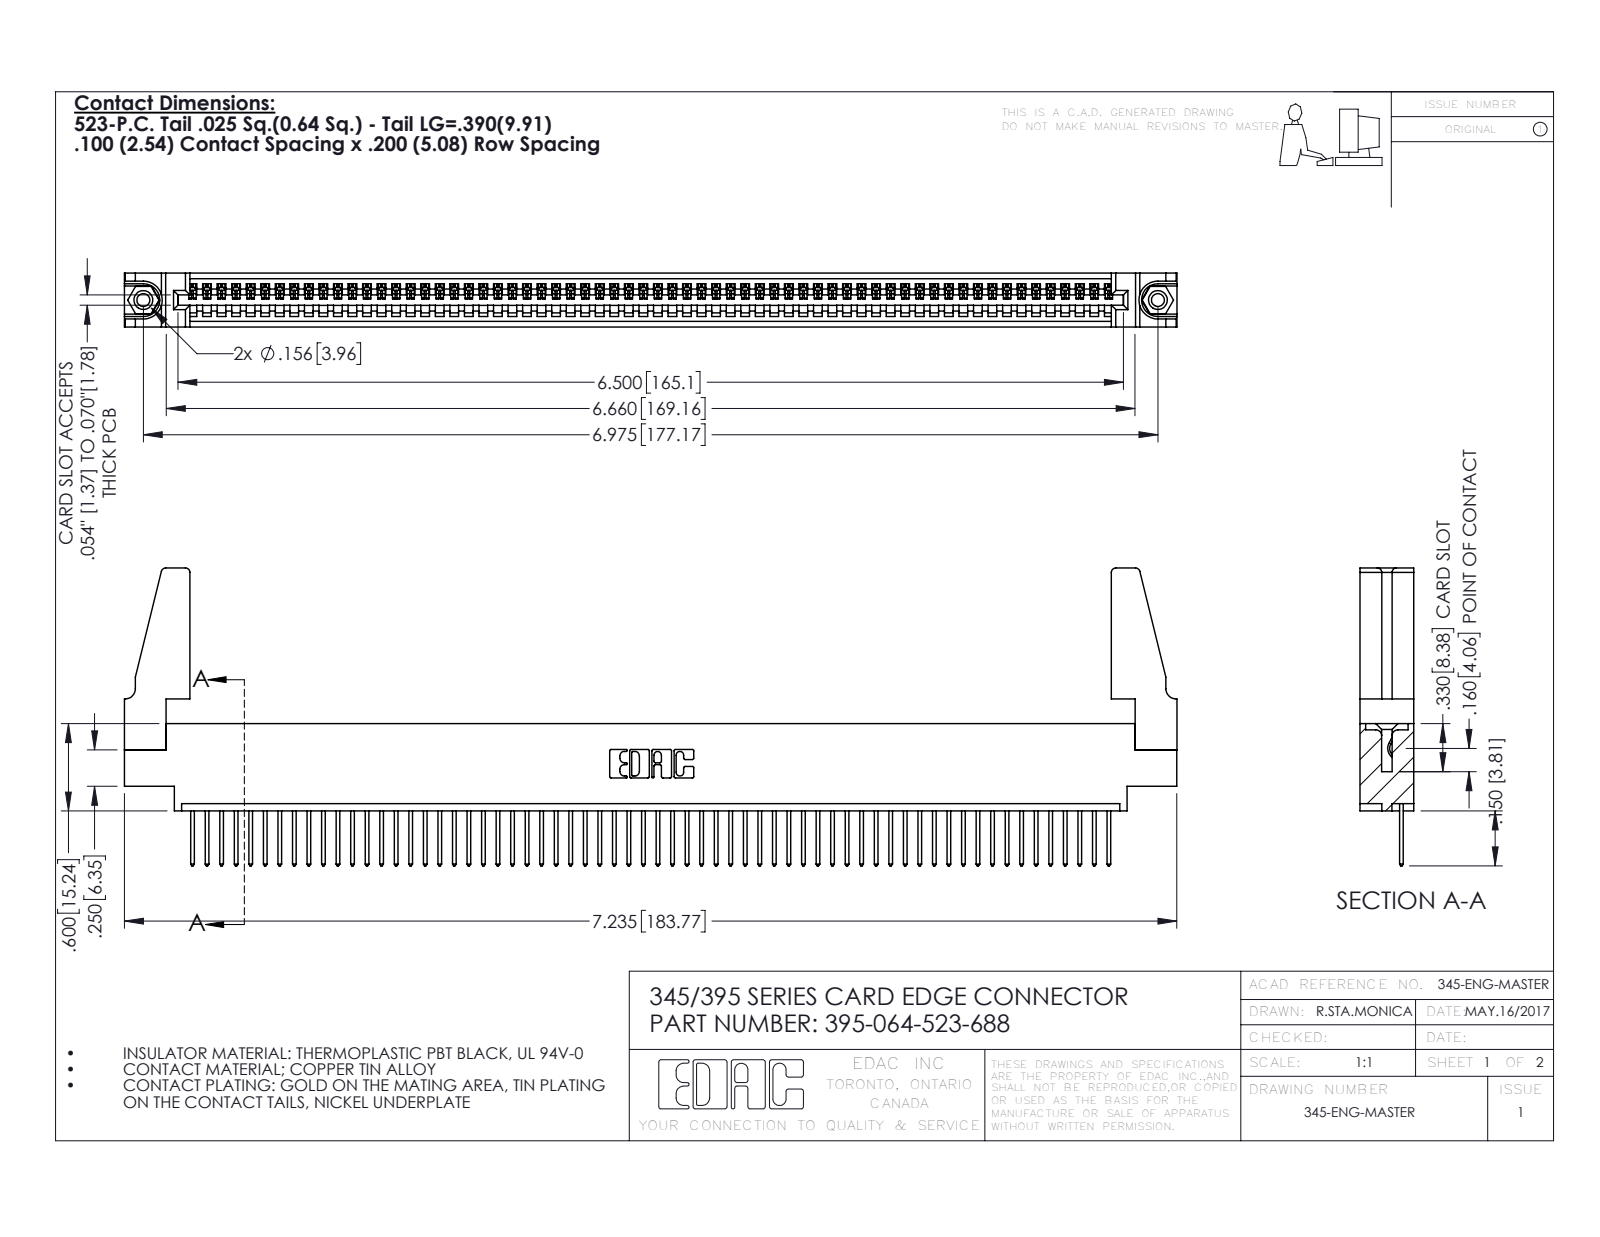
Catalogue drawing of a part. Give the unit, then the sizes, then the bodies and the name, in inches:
Units: inches
Overall size (bounding box): 7.236 × 2.047 × 0.37
Round holes (diameter × count): ⌀0.089 ×2, ⌀0.125 ×2, ⌀0.156 ×2, ⌀0.064 ×1
Round bosses / shafts (diameter × count): ⌀0.155 ×2
Partial cylindrical surfaces — rounded edges, fillets, slot ends (radius × count): R0.006 ×128, R0.01 ×128, R0.01 ×22, R0.03 ×8, R0.007 ×6, R0.031 ×6, R0.026 ×3, R0.031 ×2
Main face-to-face distances: 0.072, 0.298, 0.37, 0.098, 0.272, 0.025, 0.2, 0.225, 0.175, 0.149
Hole centre spacings: 0.27, 6.739, 6.975
Volume: 1.266 in³ · Surface area: 41.66 in²
Bodies: 69 solids, 3966 faces (2716 planar, 1234 cylindrical, 16 other)
Part name (STEP PRODUCT): 395-064-523-688; 345-220-078_345-220-088; 345-292-001_345-293-123; 345-250-001_345-250-001-102 (+1 more)
STEP written by: SolidWorks 2016 (CONFIG_CONTROL_DESIGN)
